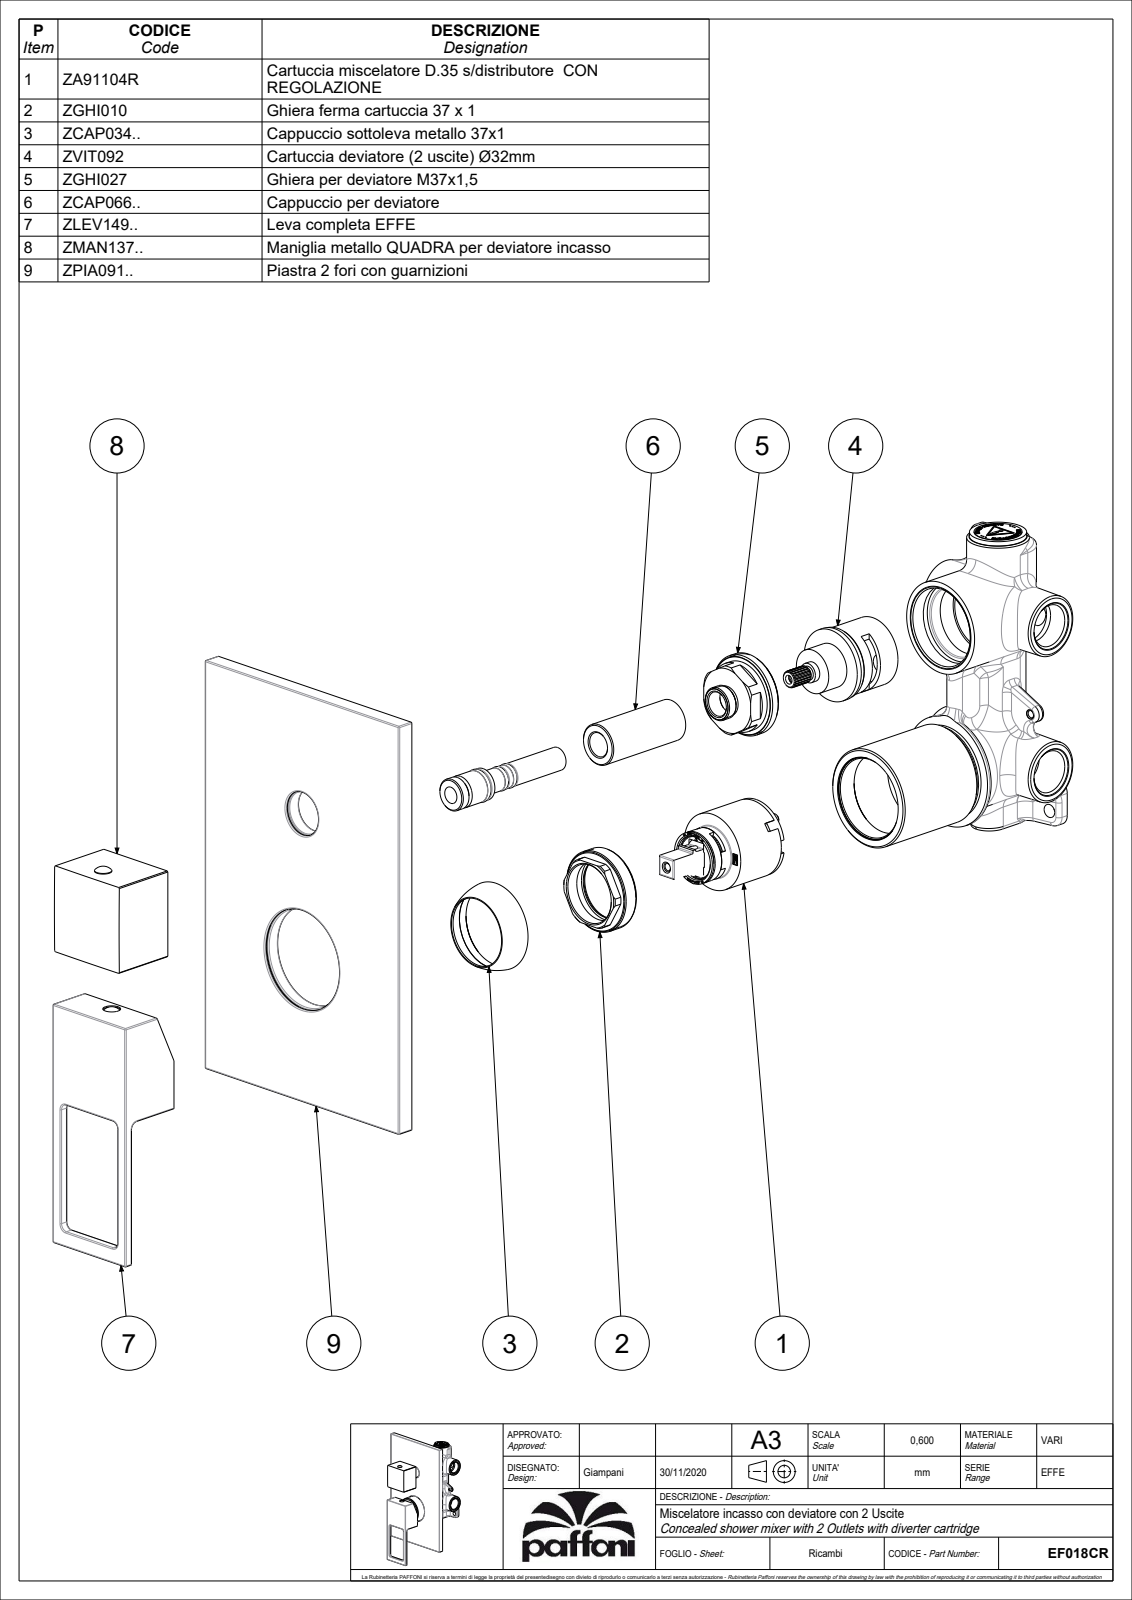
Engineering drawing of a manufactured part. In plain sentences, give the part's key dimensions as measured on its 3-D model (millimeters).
The part is named "EF018CR". Its 3-D file was written by "CREO PARAMETRIC BY PTC INC, 2020044 (CONFIG_CONTROL_DESIGN)". It is 4 solids with 1265 faces: 743 planar, 331 cylindrical and 191 other. Overall it measures 212.5 by 120 by 61.39 millimeters. Its volume is 207 185 cubic millimeters and its surface area 117 386 square millimeters. Round holes: 2 of diameter 3, 2 of diameter 4, 2 of diameter 4.5, 2 of diameter 5.5, 2 of diameter 36, 1 of diameter 3.2, 1 of diameter 4.2, 1 of diameter 5, 1 of diameter 7.8, 1 of diameter 8, 1 of diameter 11, 1 of diameter 14.8. Round bosses or shafts: 2 of diameter 7.6, 1 of diameter 51, 1 of diameter 49, 1 of diameter 44.8, 1 of diameter 35, 1 of diameter 32.2, 1 of diameter 25, 1 of diameter 23.5. Partial cylindrical surfaces (rounded edges, fillets, slot ends): 51 of radius 0.5, 11 of radius 0.15, 10 of radius 1, 5 of radius 3, 4 of radius 0.3, 1 of radius 3.85, 1 of radius 4, 1 of radius 7. The main face-to-face distances are 8, 2.5, 5.5, 40, 22.5, 37.5, 42.5, 82.5, 61.1, 55.6. The hole center spacings are 3.8, 10, 11, 14.8, 58, 68.
